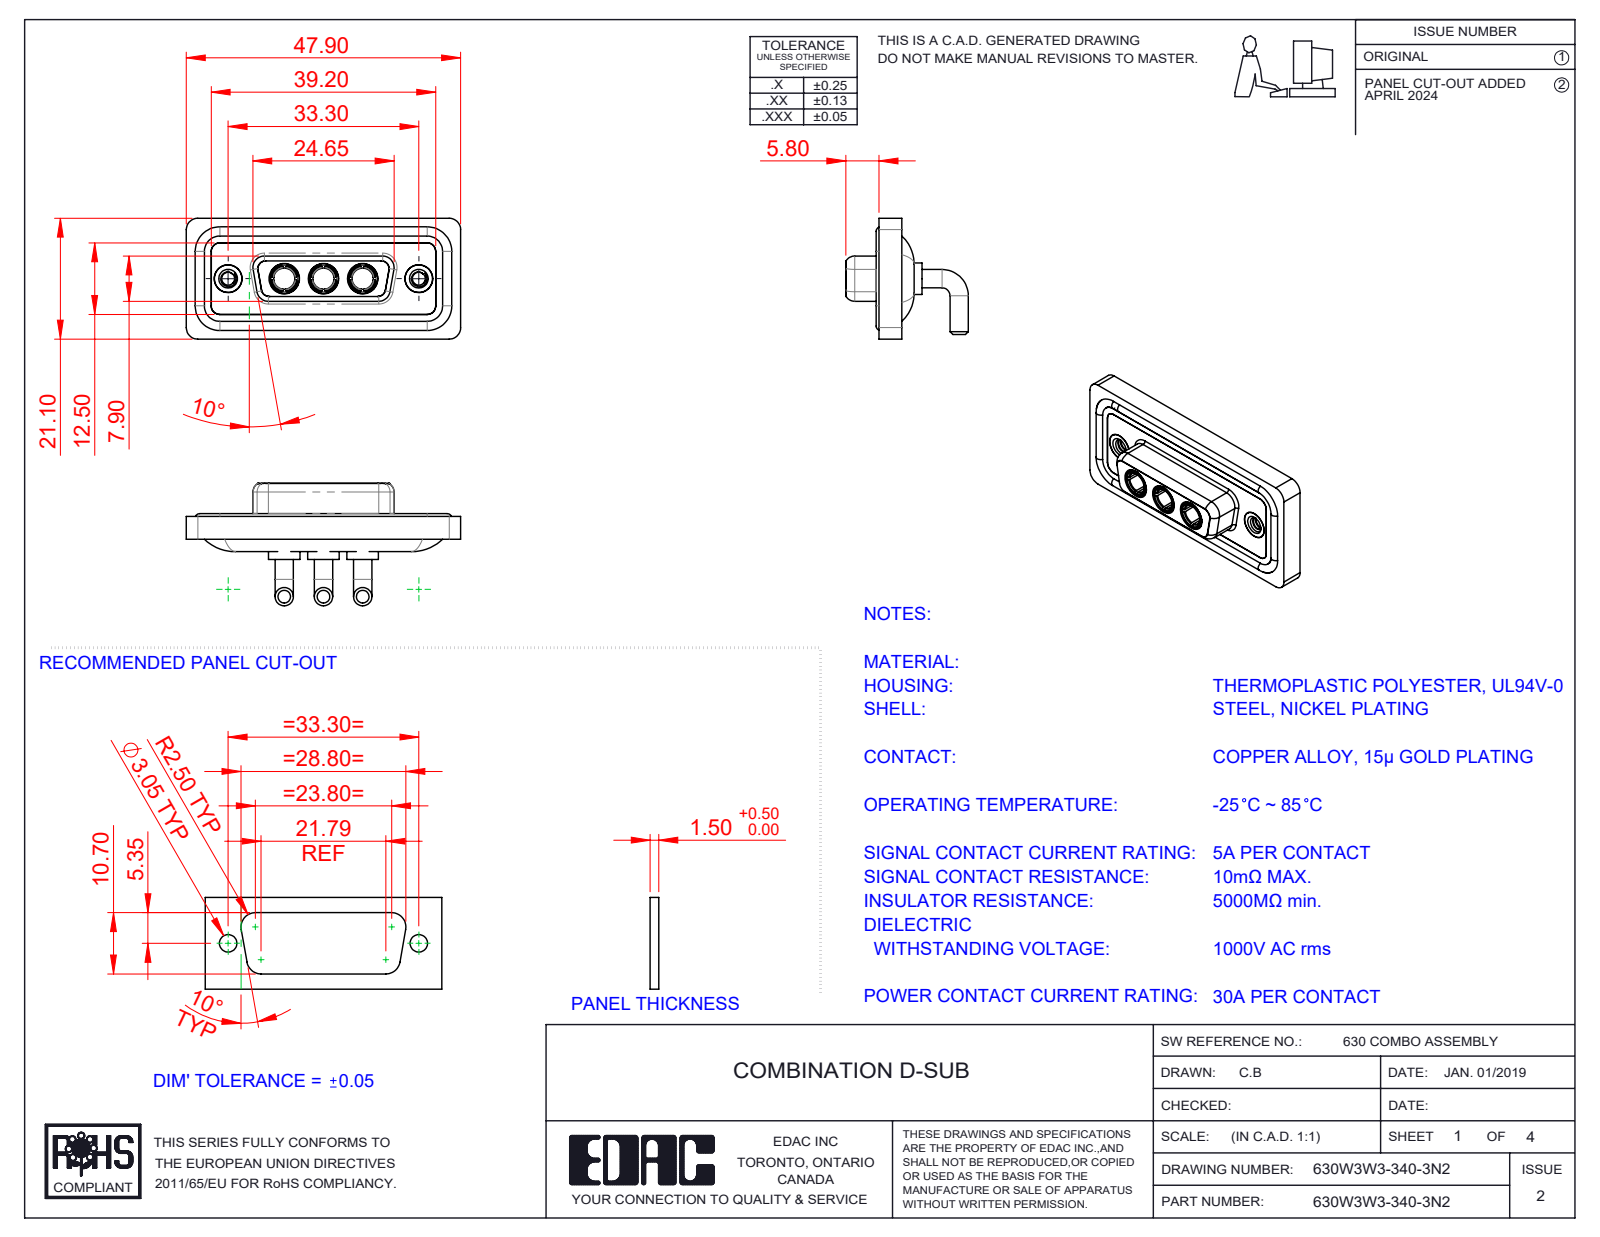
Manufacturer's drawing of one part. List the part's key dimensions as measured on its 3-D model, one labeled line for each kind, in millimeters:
Part name (STEP PRODUCT): 630Combo Shell Front_15 Contacts; 630W3W3-340-3N2; Power Socket_30A RA; 630Combo Threaded Rivet_2 (+3 more)
STEP written by: SolidWorks 2023 (CONFIG_CONTROL_DESIGN)
Units: millimetres
Bodies: 13 solids, 620 faces (192 planar, 263 cylindrical, 165 other)
Overall size (bounding box): 47.9 × 21.4 × 21.1
Volume: 6 264 mm³ · Surface area: 10 027 mm²
Round holes (diameter × count): ⌀4.85 ×5, ⌀3.7 ×3, ⌀5.3 ×3, ⌀2.26 ×2, ⌀4 ×2, ⌀4.05 ×2, ⌀5 ×2
Round bosses / shafts (diameter × count): ⌀3.2 ×6, ⌀1.6 ×4, ⌀5.5 ×3, ⌀5.2 ×3, ⌀4.96 ×3, ⌀4.75 ×3, ⌀3.75 ×3, ⌀4.95 ×2
Partial cylindrical surfaces — rounded edges, fillets, slot ends (radius × count): R2 ×20, R1.5 ×18, R1.35 ×12, R1.6 ×8, R0.25 ×4, R0.5 ×4, R0.6 ×4, R0.65 ×4
Main face-to-face distances: 0.4, 1.8, 1.1, 1.6, 2.9, 2.5, 3.1, 3.7, 4.1, 1.5
Hole centre spacings: 6.85, 9.8, 16.65, 23.5, 13.7, 33.3
